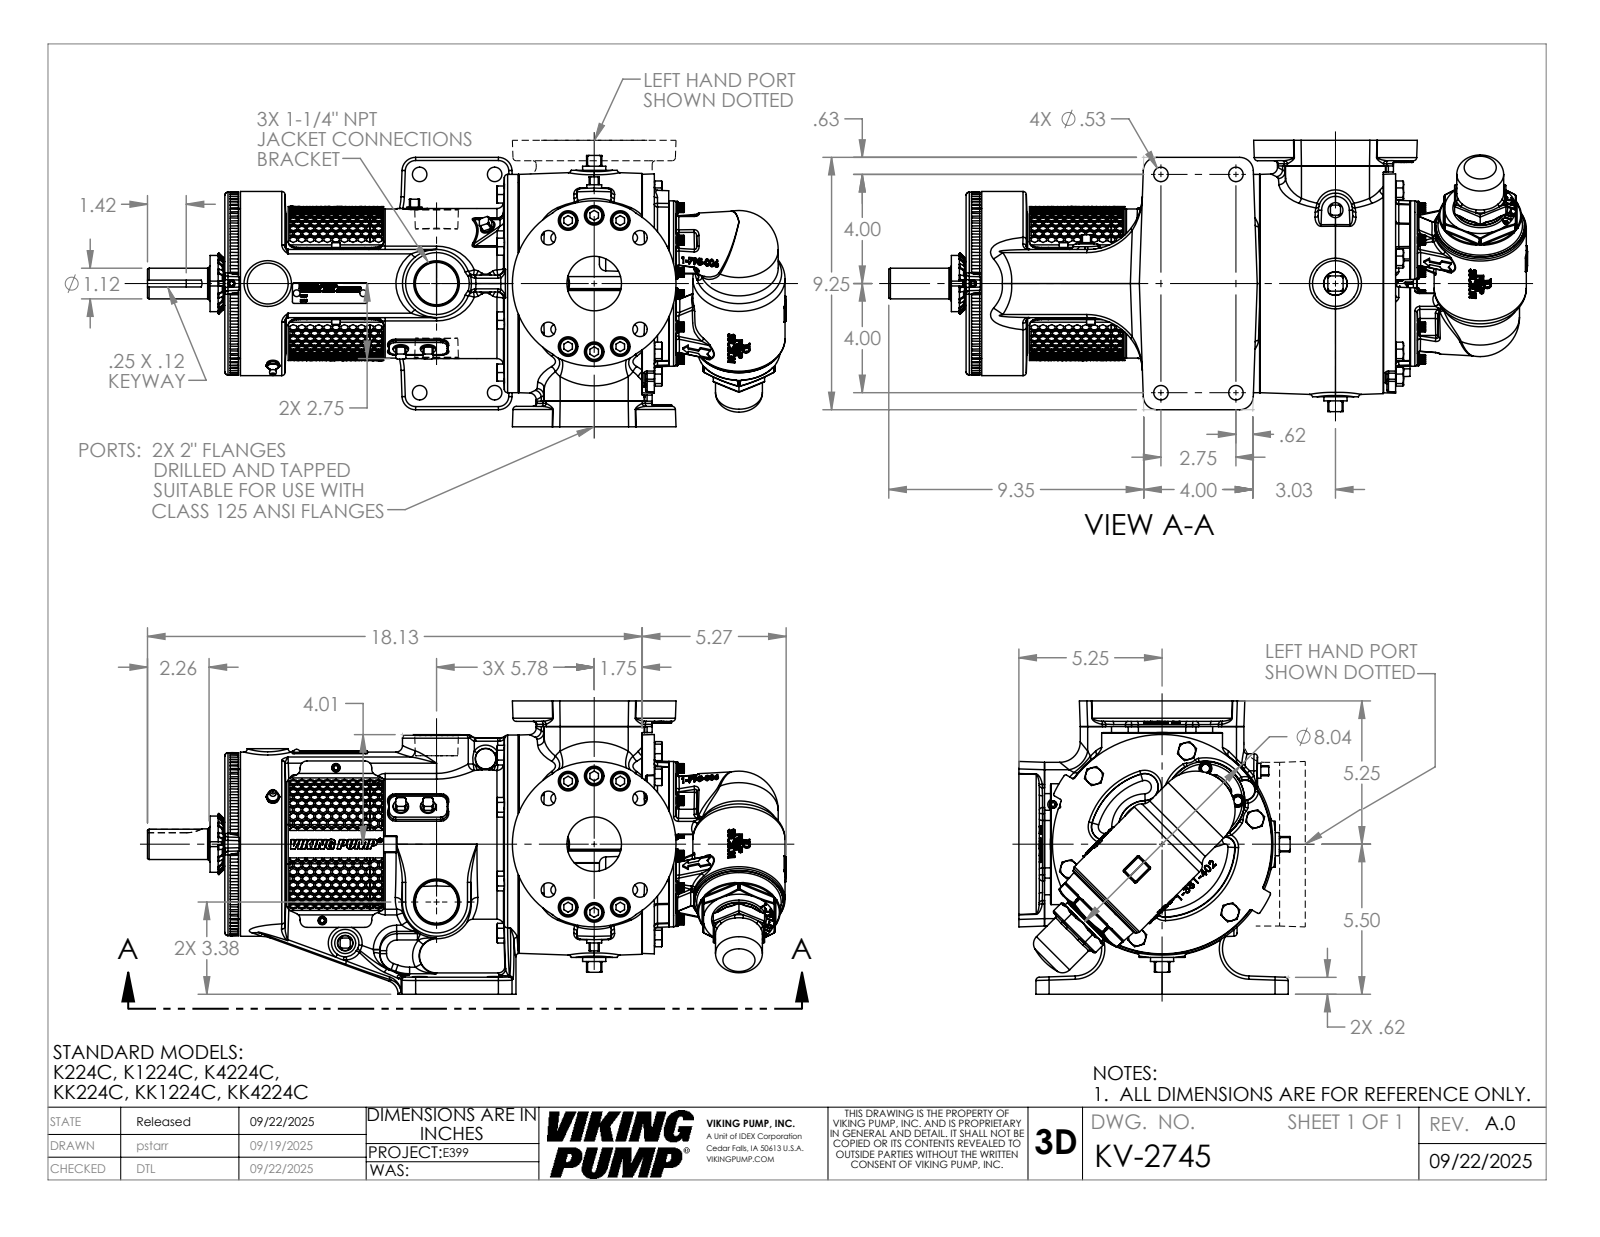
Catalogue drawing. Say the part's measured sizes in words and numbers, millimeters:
The part is named "KV-2745". Its 3-D file was written by "SolidWorks 2024 (AUTOMOTIVE_DESIGN)". It is 1 solid with 6280 faces: 2083 planar, 861 cylindrical and 3336 other. Overall it measures 594.8 by 273.1 by 252.6 millimeters. Its volume is 11 260 000 cubic millimeters and its surface area 738 100 square millimeters. Round holes: 12 of diameter 13.5, 12 of diameter 18.3, 9 of diameter 6.4, 8 of diameter 9.3, 8 of diameter 19.8, 6 of diameter 5, 2 of diameter 4, 2 of diameter 8, 2 of diameter 50.8, 1 of diameter 6.5, 1 of diameter 11.5, 1 of diameter 35.2. Round bosses or shafts: 23 of diameter 15.9, 8 of diameter 11.9, 3 of diameter 73.2, 3 of diameter 15.9, 3 of diameter 7.9, 3 of diameter 4.8, 1 of diameter 203.2, 1 of diameter 171.5. Partial cylindrical surfaces (rounded edges, fillets, slot ends): 96 of radius 0.3, 39 of radius 3, 37 of radius 0.8, 22 of radius 6.1, 18 of radius 25.4, 16 of radius 3, 8 of radius 2.3, 8 of radius 4.5. The main face-to-face distances are 273.1, 101.6, 264.8, 135.2, 400, 14.6, 120.7, 385.4, 63.5, 12.7. The hole center spacings are 76.2, 26.2, 63.5, 6.9, 24.8, 35, 55.5, 60.6.
